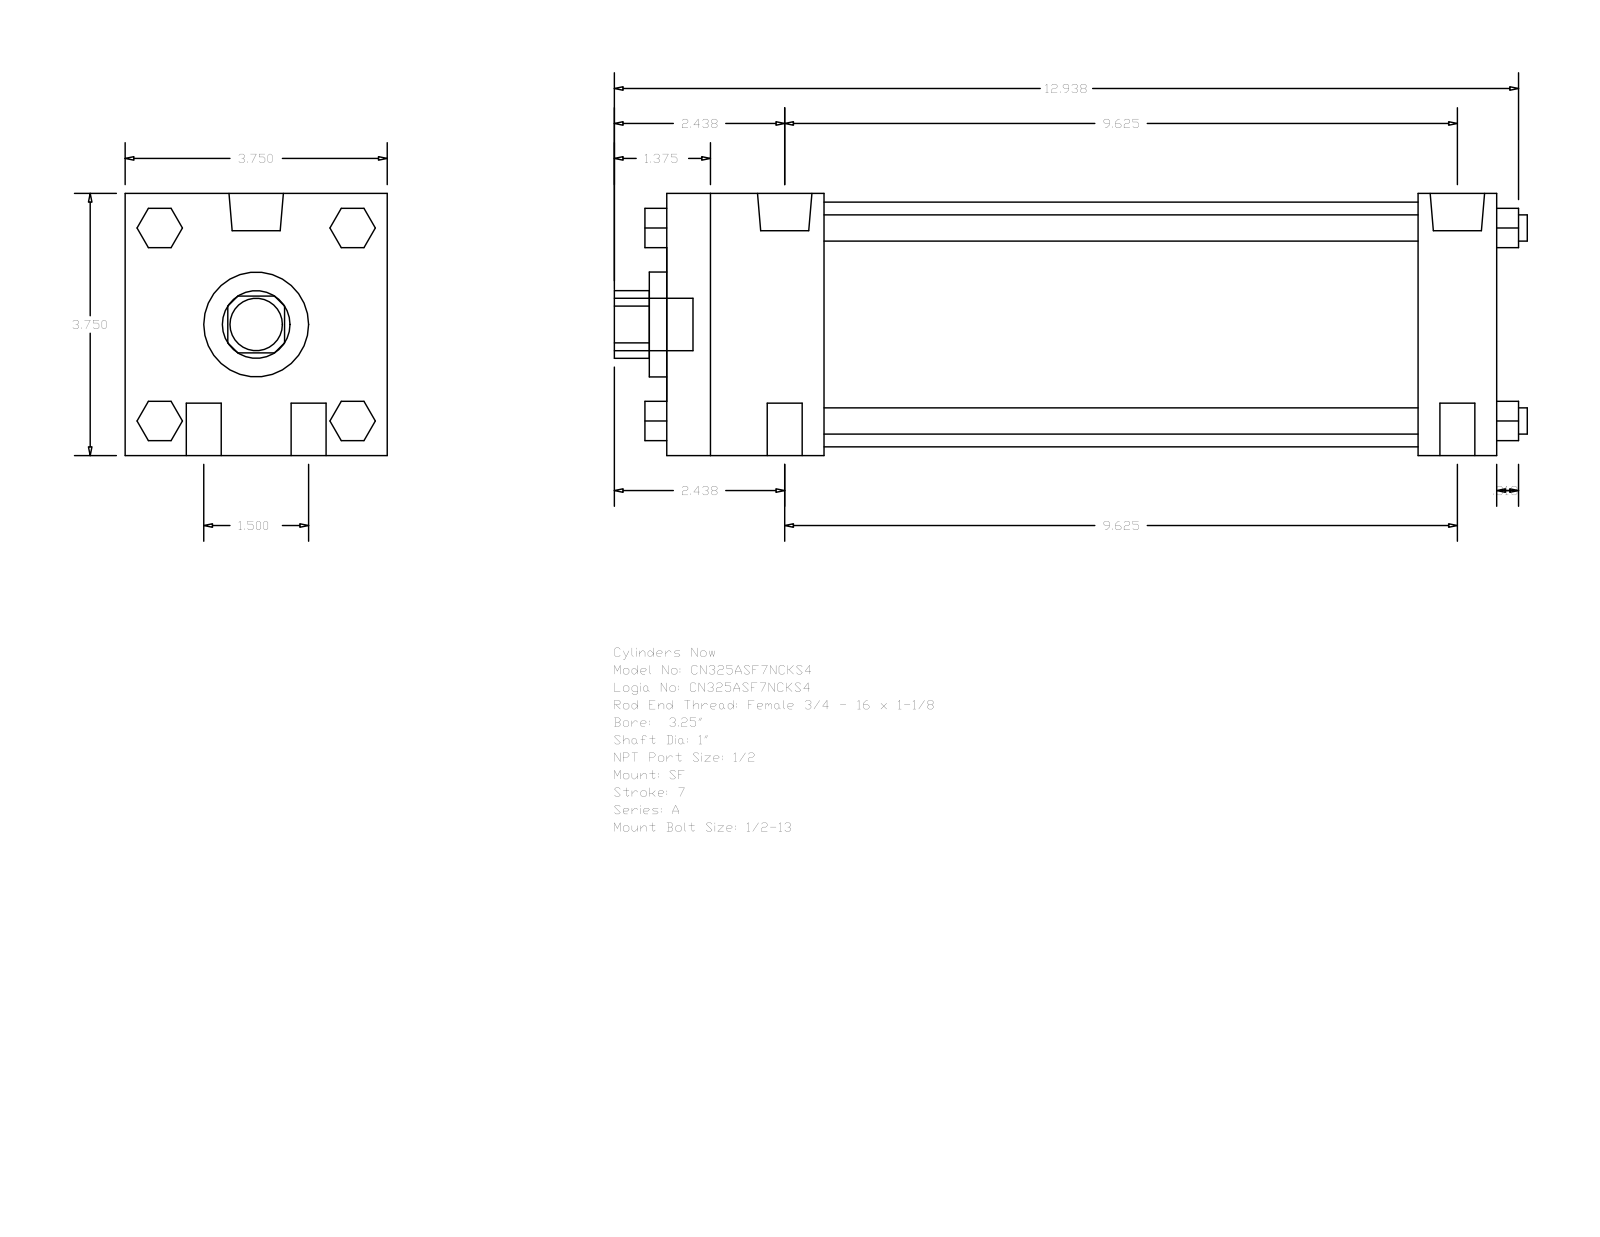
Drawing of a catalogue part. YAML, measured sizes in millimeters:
part_name: "A_SF__0325_1"
step_written_by: "GSSL Pune (CONFIG_CONTROL_DESIGN)"
units: millimeters
bodies: {solids: 0, faces: 124, planar: 94, cylindrical: 30, other: 0}
overall_size: [331.79, 95.25, 95.25]
round_holes:
  - {diameter: 25.4, count: 1}
  - {diameter: 38.1, count: 1}
  - {diameter: 88.9, count: 1}
round_bosses_or_shafts:
  - {diameter: 12.7, count: 4}
  - {diameter: 9.53, count: 4}
  - {diameter: 19.77, count: 2}
  - {diameter: 8.73, count: 2}
  - {diameter: 19.05, count: 1}
partial_cylinders:
  - {radius: 12.29, count: 1}
face_to_face_distances: [95.24, 301.63, 273.05, 28.58, 57.15, 215.9, 244.48, 14.28, 35.05, 60.71]
